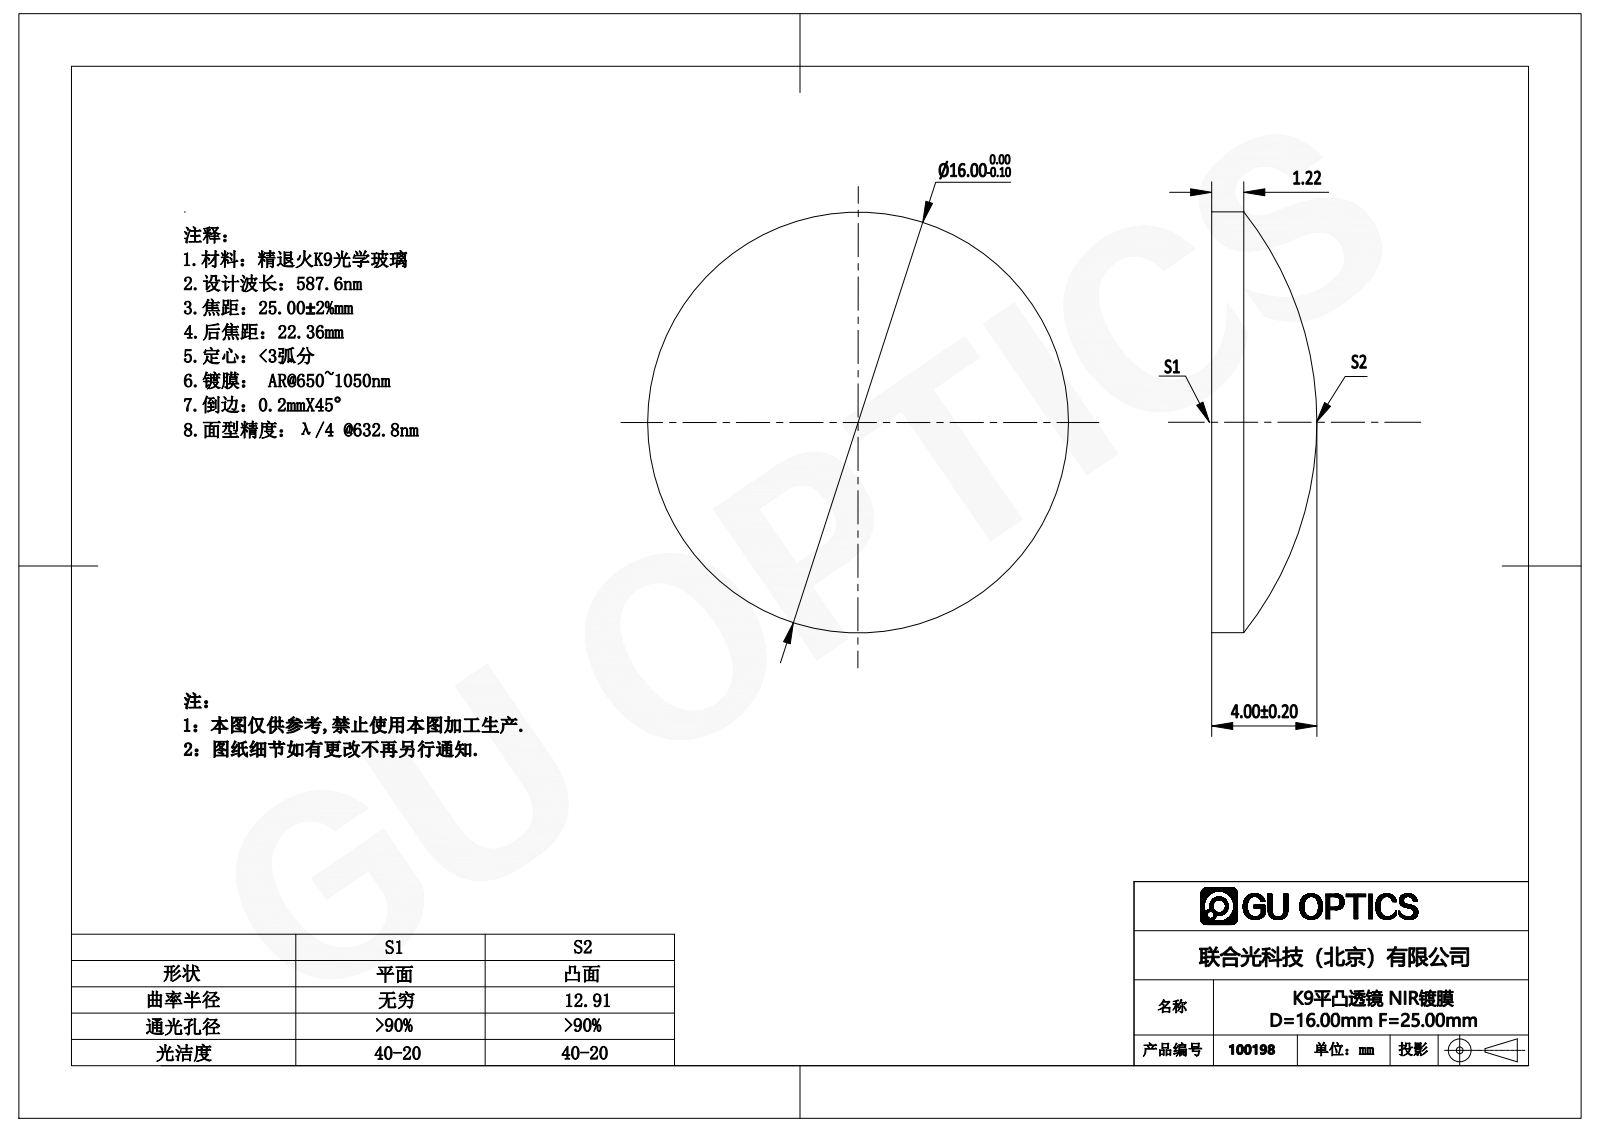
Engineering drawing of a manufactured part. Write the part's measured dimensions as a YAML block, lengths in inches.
part_name: "100198"
step_written_by: "SolidWorks 2016 (AUTOMOTIVE_DESIGN)"
units: inches
bodies: {solids: 1, faces: 5, planar: 1, cylindrical: 2, other: 2}
overall_size: [0.63, 0.63, 0.157]
volume: 0.033
surface_area: 0.756
round_bosses_or_shafts:
  - {diameter: 0.63, count: 1}
